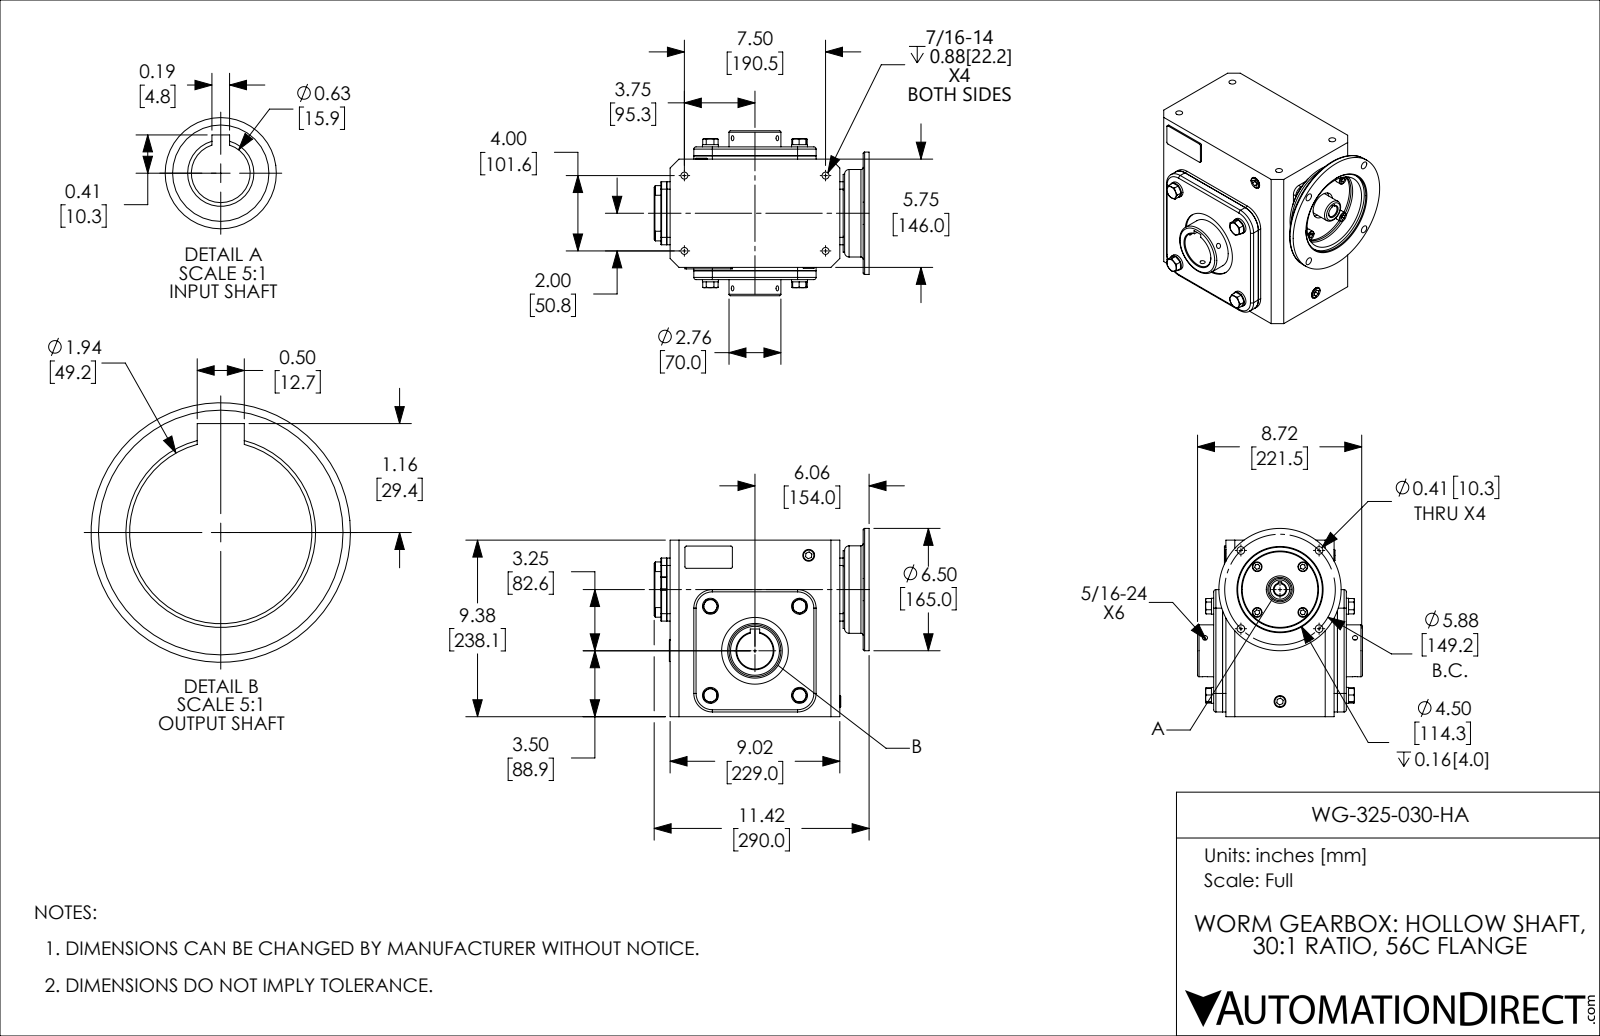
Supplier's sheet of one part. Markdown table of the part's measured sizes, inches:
| quantity | value |
| --- | --- |
| part name | WG-325-030-HA |
| STEP written by | SolidWorks 2017 (AUTOMOTIVE_DESIGN) |
| units | inches |
| bodies | 39 solids, 587 faces (314 planar, 178 cylindrical, 95 other) |
| overall size | 11.417 × 9.998 × 8.76 |
| volume | 515.8 in³ |
| surface area | 982.1 in² |
| round holes (diameter × count) | 0.272 × 6, 0.368 × 4, 0.406 × 4, 0.628 × 3, 0.591 × 1, 0.625 × 1, 0.978 × 1, 1.181 × 1, 1.457 × 1, 1.937 × 1, 2.441 × 1, 2.756 × 1 |
| round bosses / shafts (diameter × count) | 0.846 × 4, 0.512 × 4, 6.496 × 1, 4.646 × 1, 4.134 × 1, 2.835 × 1, 1.142 × 1 |
| partial cylindrical surfaces (radius × count) | 0.118 × 8, 0.079 × 7, 0.394 × 4, 0.906 × 4, 0.984 × 4, 0.02 × 2, 0.039 × 2 |
| main face-to-face distances | 0.079, 0.177, 6.496, 0.394, 0.571, 6.319, 5.925, 6.398, 6.969, 0.472 |
| hole center spacings | 2.937, 4.154, 4.244, 7.064, 7.972, 2.385, 4, 4.389 |
